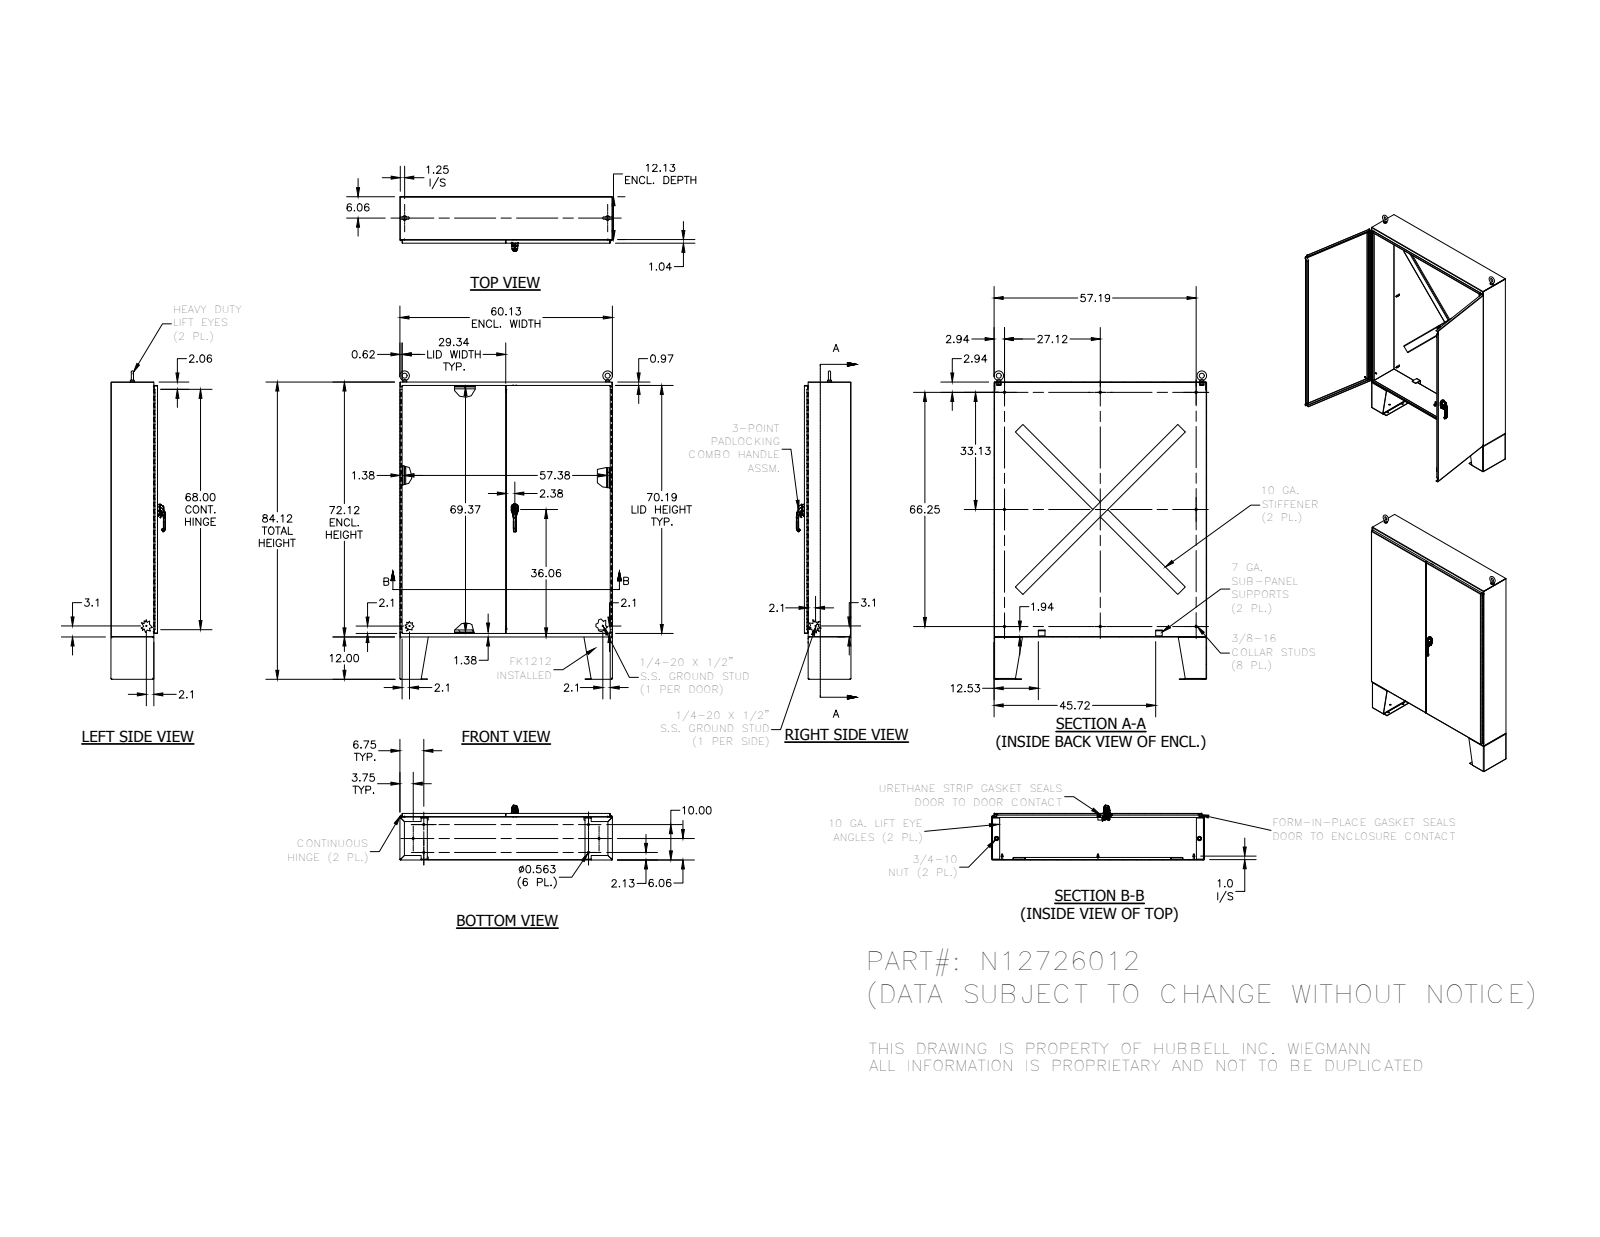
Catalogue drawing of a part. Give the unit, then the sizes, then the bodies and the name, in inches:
Units: inches
Overall size (bounding box): 87.248 × 60.125 × 15.338
Round holes (diameter × count): ⌀0.563 ×18, ⌀0.277 ×8, ⌀0.2 ×4, ⌀0.28 ×3, ⌀0.125 ×2, ⌀0.125 ×2, ⌀0.241 ×2, ⌀0.25 ×2, ⌀0.252 ×2, ⌀0.4 ×2, ⌀0.45 ×2, ⌀0.642 ×2
Round bosses / shafts (diameter × count): ⌀0.33 ×8, ⌀0.625 ×5, ⌀0.25 ×5, ⌀0.625 ×3, ⌀0.337 ×3, ⌀1.25 ×2, ⌀1.12 ×2, ⌀1 ×2
Partial cylindrical surfaces — rounded edges, fillets, slot ends (radius × count): R0.031 ×24, R0.094 ×23, R0.219 ×22, R0.05 ×18, R0.025 ×16, R0.125 ×15, R0.03 ×13, R0.067 ×8
Main face-to-face distances: 0.094, 13.067, 12.973, 13.16, 60.031, 72.031, 60.125, 59.938, 0.125, 71.938
Hole centre spacings: 2.041, 4.95, 5, 6.688, 6.901, 6.992, 10.75, 11.856
Volume: 1 488 in³ · Surface area: 30 053 in²
Bodies: 76 solids, 2596 faces (1528 planar, 768 cylindrical, 300 other)
Part name (STEP PRODUCT): N12726012
STEP written by: SolidWorks 2018 (AUTOMOTIVE_DESIGN)
